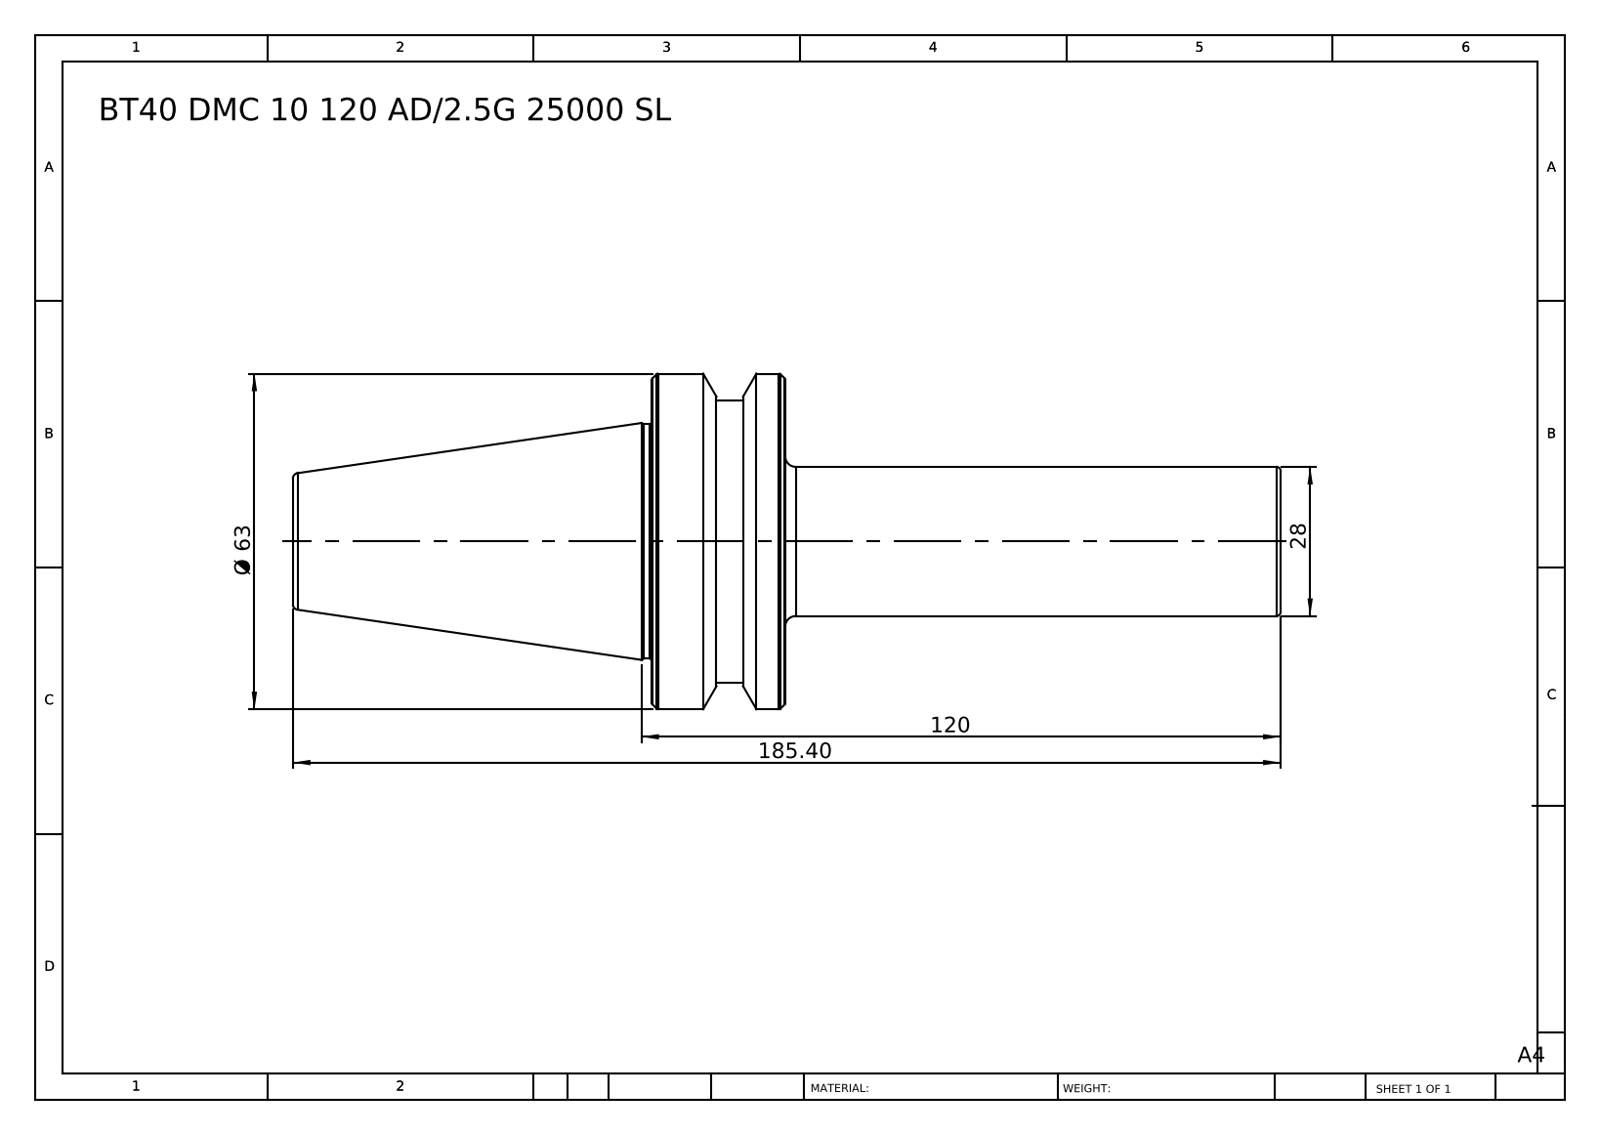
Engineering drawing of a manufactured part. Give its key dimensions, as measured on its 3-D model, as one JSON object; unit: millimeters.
{"part_name": "BT40 DMC 10 120 AD-2.5G 25000 SL", "step_written_by": "SolidWorks 2014 (CONFIG_CONTROL_DESIGN)", "units": "millimeters", "bodies": {"solids": 1, "faces": 44, "planar": 6, "cylindrical": 10, "other": 28}, "overall_size": [185.4, 63, 63], "volume_mm3": 195673, "surface_area_mm2": 26397, "round_bosses_or_shafts": [[63, 1], [53, 1], [44, 1], [28, 1]], "face_to_face_distances": [25, 93, 118, 185.4, 92.4, 67.4, 100.9, 7.9, 17.1, 84.5]}
